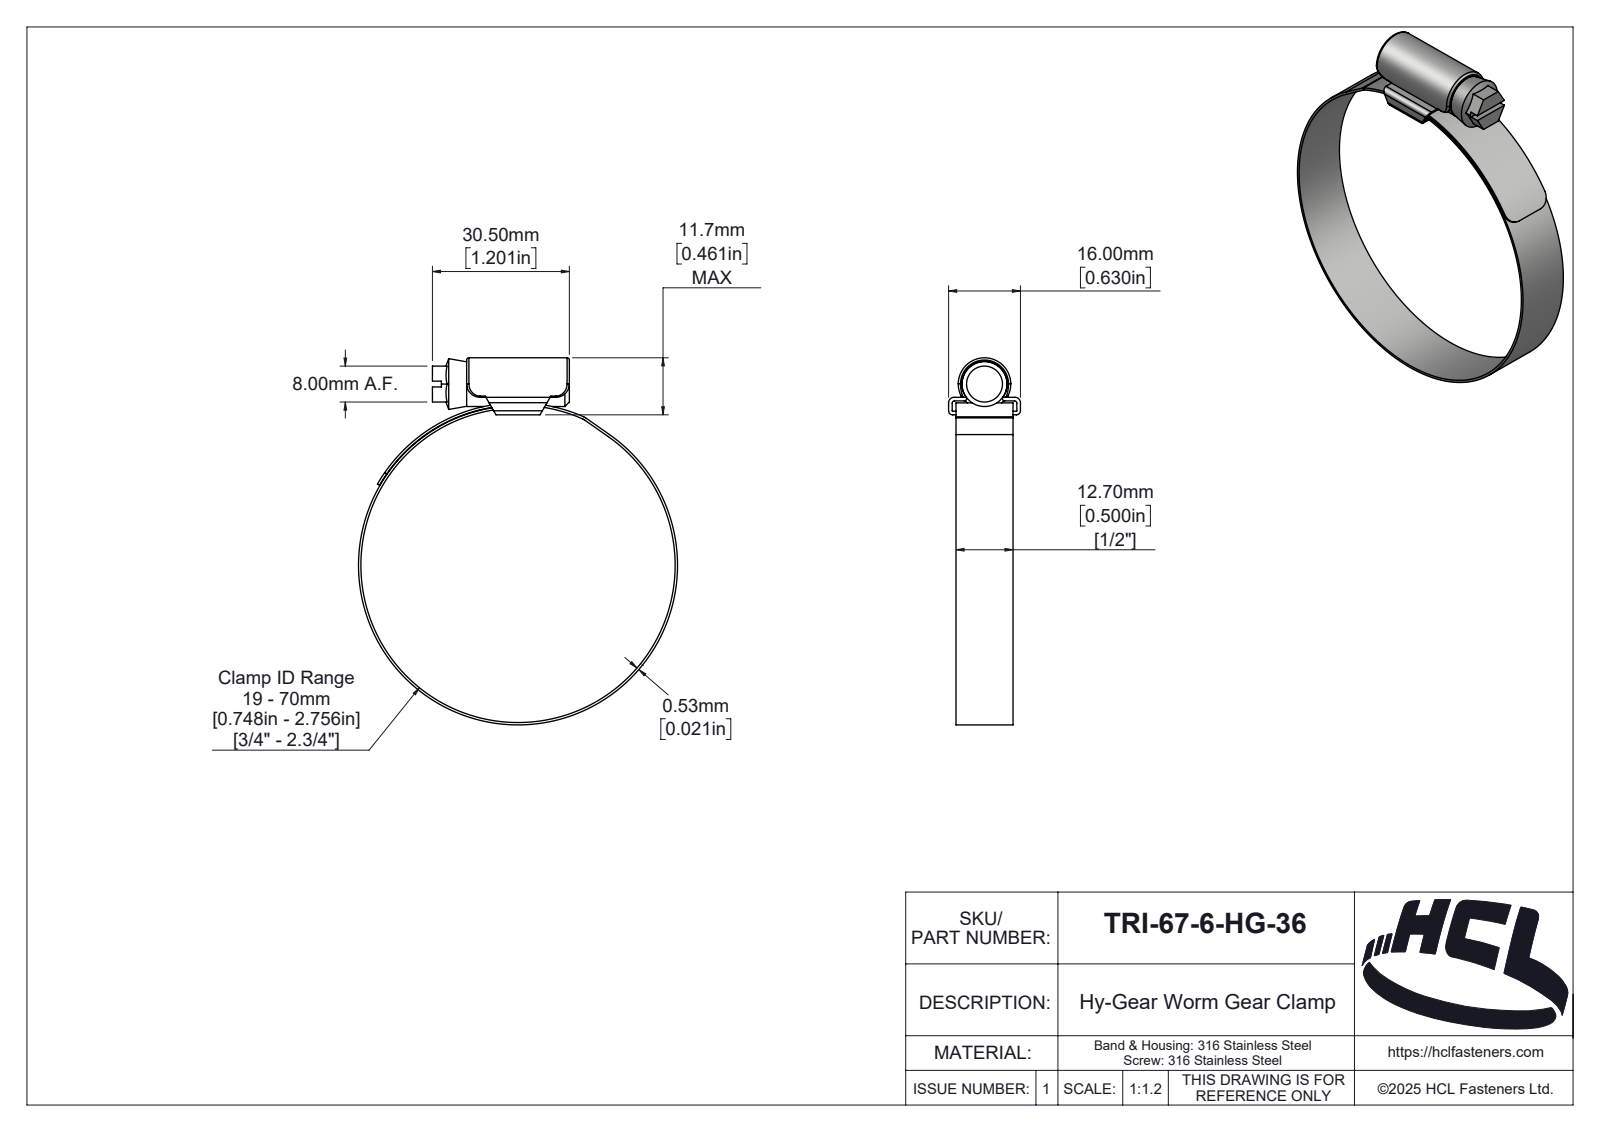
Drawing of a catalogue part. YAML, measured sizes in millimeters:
part_name: "TRI-57-0-HG-36"
step_written_by: "SolidWorks 2025 (AUTOMOTIVE_DESIGN)"
units: millimeters
bodies: {solids: 3, faces: 189, planar: 39, cylindrical: 89, other: 61}
overall_size: [81.73, 71.06, 16]
volume: 4737
surface_area: 9770
round_holes:
  - {diameter: 70, count: 1}
round_bosses_or_shafts:
  - {diameter: 71.06, count: 1}
  - {diameter: 10, count: 1}
partial_cylinders:
  - {radius: 0.5, count: 6}
  - {radius: 3, count: 4}
  - {radius: 0.1, count: 2}
  - {radius: 0.9, count: 2}
  - {radius: 1.2, count: 2}
  - {radius: 0.46, count: 1}
  - {radius: 1.89, count: 1}
  - {radius: 2, count: 1}
face_to_face_distances: [0.8, 12.7, 3.1, 0.53, 2.3, 3.9, 30.5, 1.65, 14.35, 15.2]
